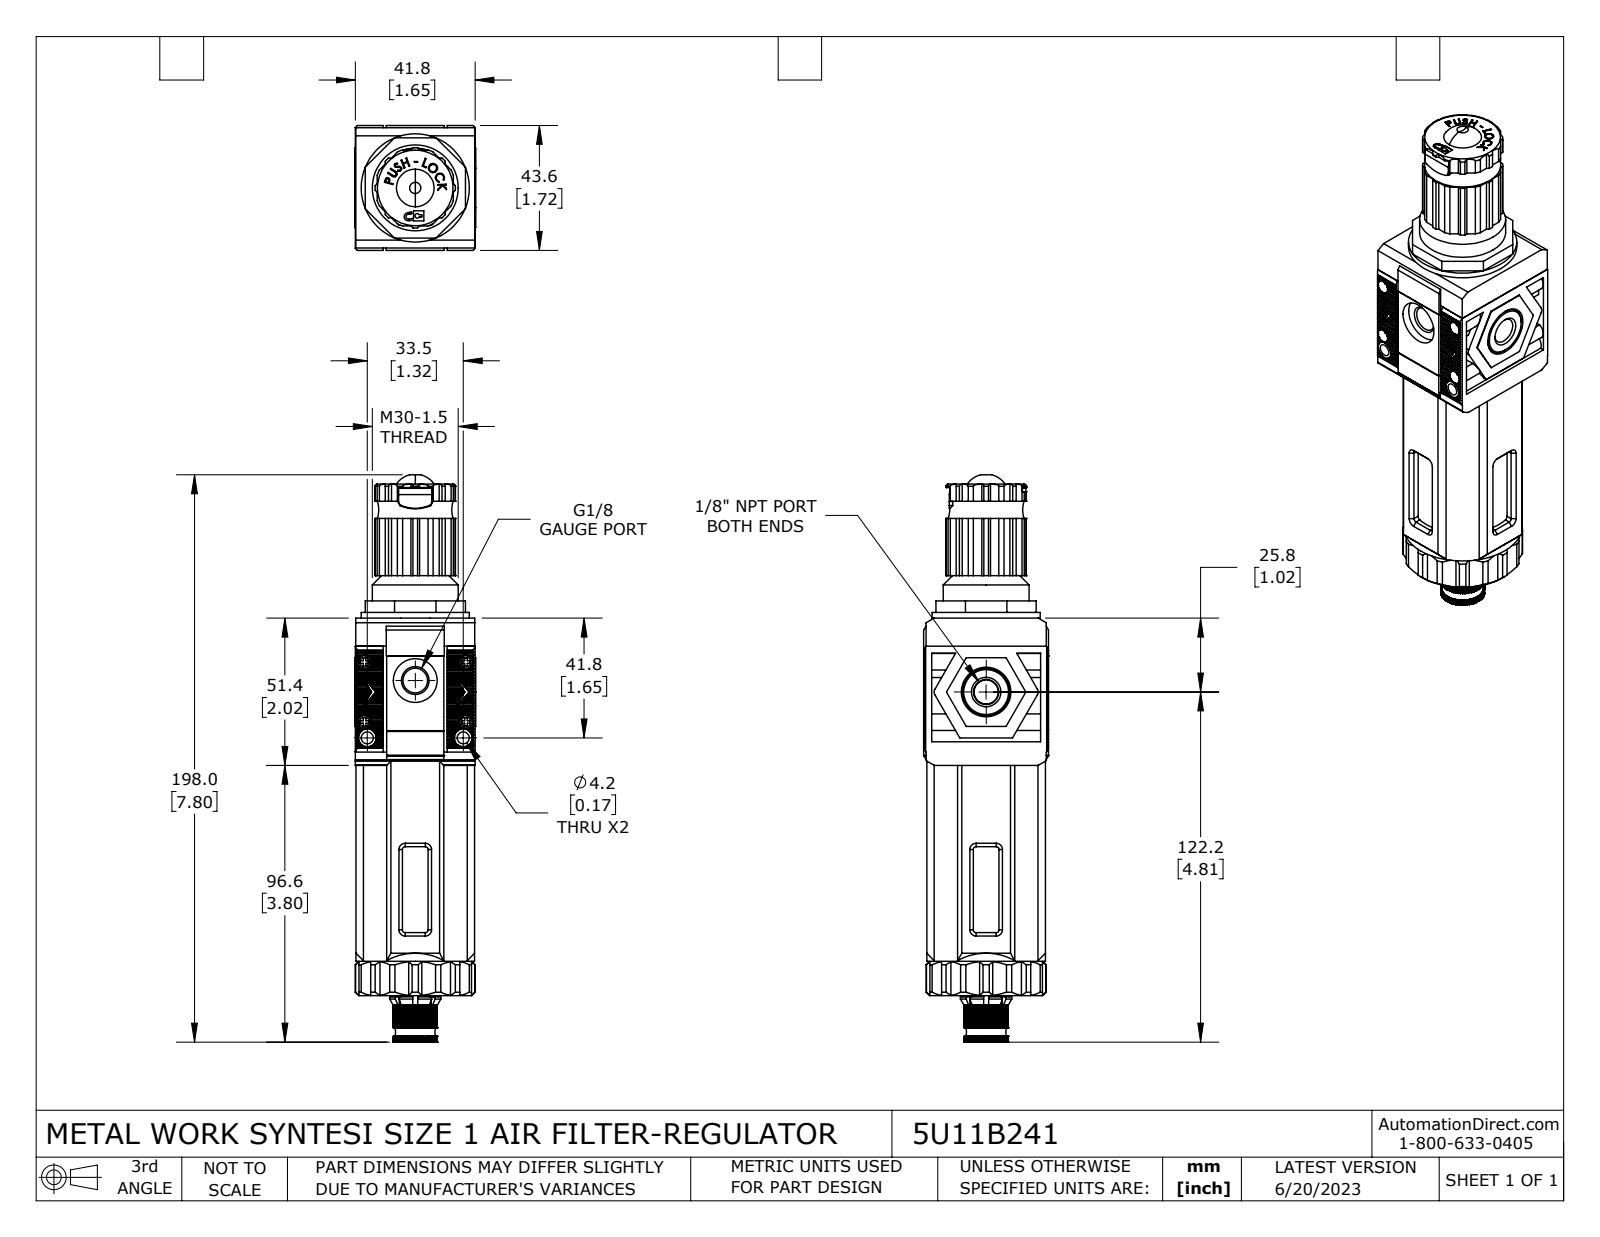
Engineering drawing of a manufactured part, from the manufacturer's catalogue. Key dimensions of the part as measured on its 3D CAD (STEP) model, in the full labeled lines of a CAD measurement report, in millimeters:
Part name (STEP PRODUCT): 5U11B241
STEP written by: SolidWorks 2021 (CONFIG_CONTROL_DESIGN)
Units: millimetres
Bodies: 15 solids, 2181 faces (1612 planar, 418 cylindrical, 151 other)
Overall size (bounding box): 198 × 43.6 × 42.2
Volume: 162 100 mm³ · Surface area: 74 390 mm²
Round holes (diameter × count): ⌀2.1 ×4, ⌀3 ×4, ⌀4.7 ×4, ⌀3.5 ×2, ⌀4.2 ×2, ⌀2.4 ×1, ⌀3.2 ×1, ⌀6.4 ×1, ⌀7 ×1, ⌀8.6 ×1, ⌀8.7 ×1, ⌀15.3 ×1
Round bosses / shafts (diameter × count): ⌀4.6 ×4, ⌀2.6 ×4, ⌀6.2 ×2, ⌀41.4 ×1, ⌀37.8 ×1, ⌀35.6 ×1, ⌀25 ×1, ⌀22.8 ×1
Partial cylindrical surfaces — rounded edges, fillets, slot ends (radius × count): R1 ×9, R0.6 ×4, R3.1 ×4, R1.5 ×3, R0.2 ×2, R1.3 ×2, R2 ×2, R0.4 ×1
Main face-to-face distances: 41.6, 41.4, 1.1, 41.8, 42.5, 7.8, 34, 7.6, 33.8, 41.7
Hole centre spacings: 5.6, 9.2, 18.8, 19.9, 20.9, 22.9, 26.1, 26.5
